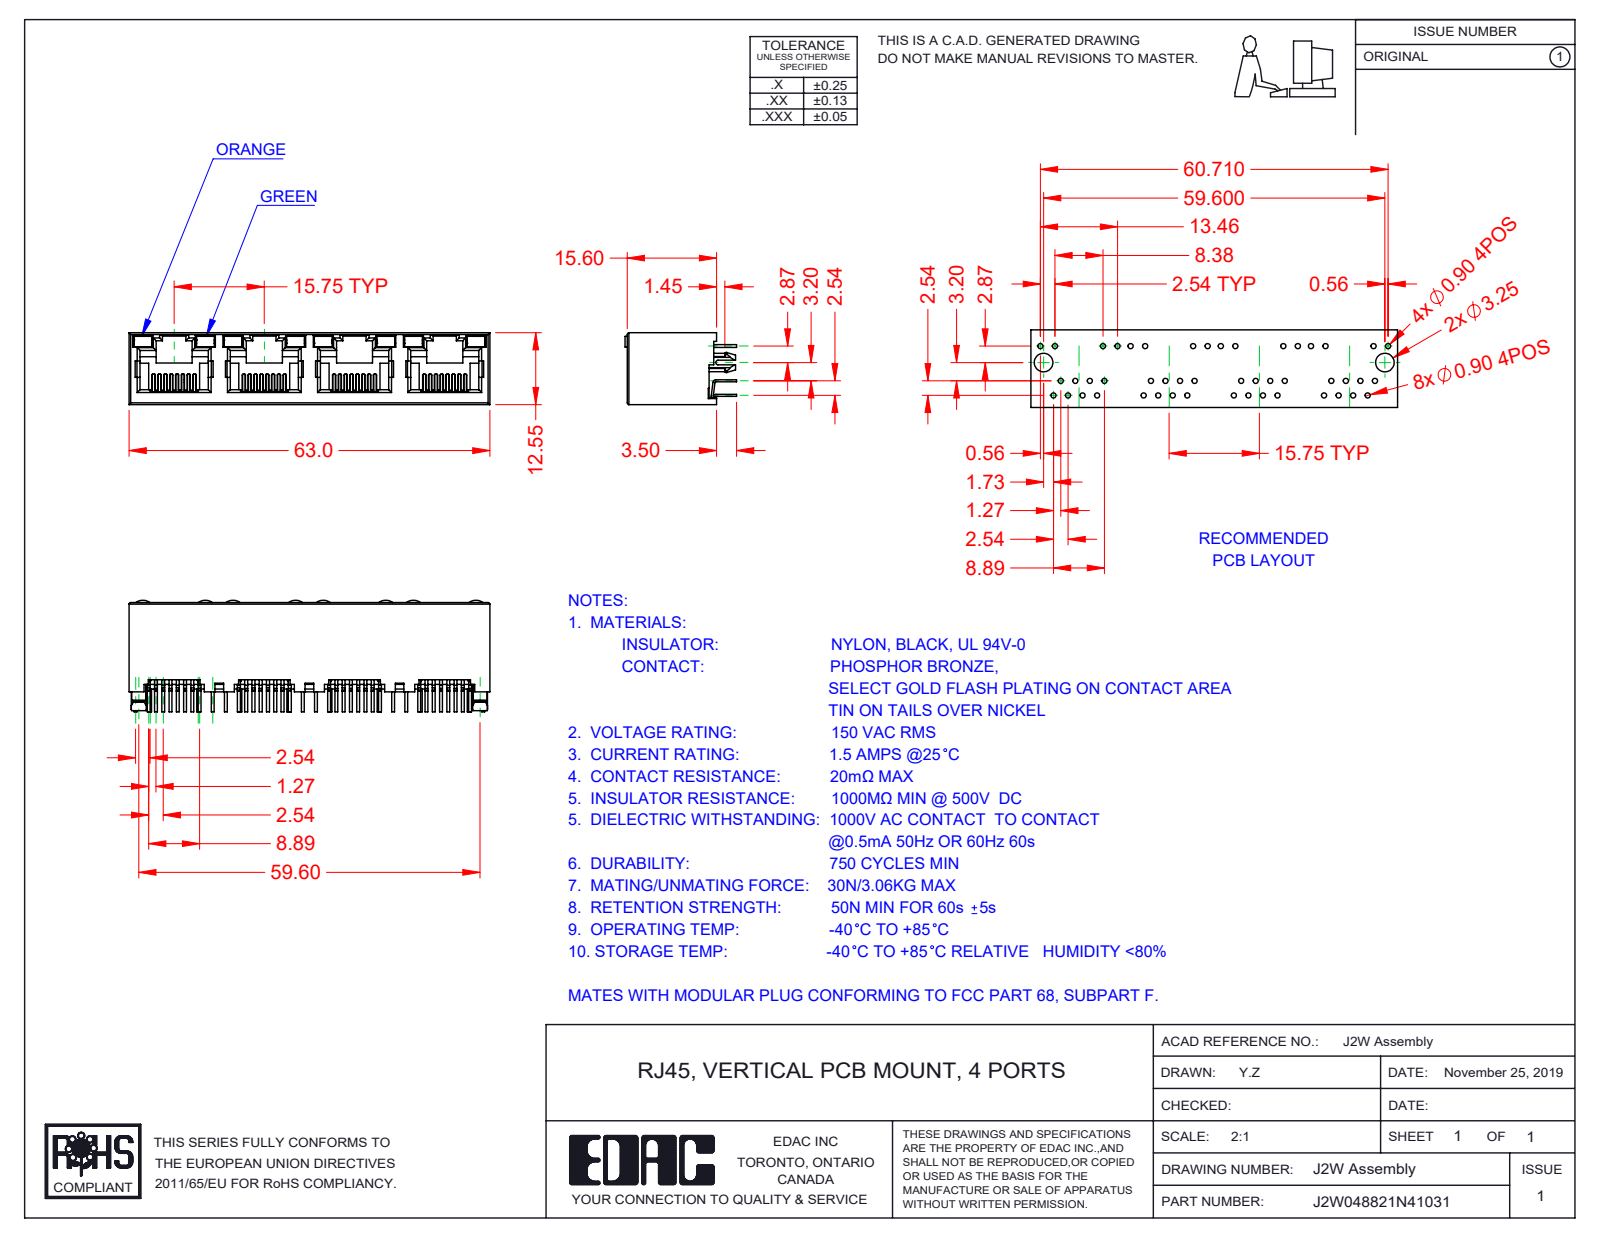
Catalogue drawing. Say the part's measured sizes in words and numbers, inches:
The part is named "2W LED LH_4-Orange; 2W Contacts; 2W Contact Lock; 2W Insulator (+2 more)". Its 3-D file was written by "SolidWorks 2016 (CONFIG_CONTROL_DESIGN)". It is 45 solids with 3135 faces: 2600 planar, 477 cylindrical and 58 other. Overall it measures 2.48 by 0.768 by 0.494 inches. Its volume is 0.326 cubic inches and its surface area 20.37 square inches. Partial cylindrical surfaces (rounded edges, fillets, slot ends): 64 of radius 0.006, 29 of radius 0.008, 28 of radius 0.02, 14 of radius 0.012, 8 of radius 0.018, 8 of radius 0.079, 2 of radius 0.01, 2 of radius 0.059. The main face-to-face distances are 0.494, 0.469, 0.026, 0.62, 0.014, 0.059, 0.031, 0.024, 0.445, 1.24.
